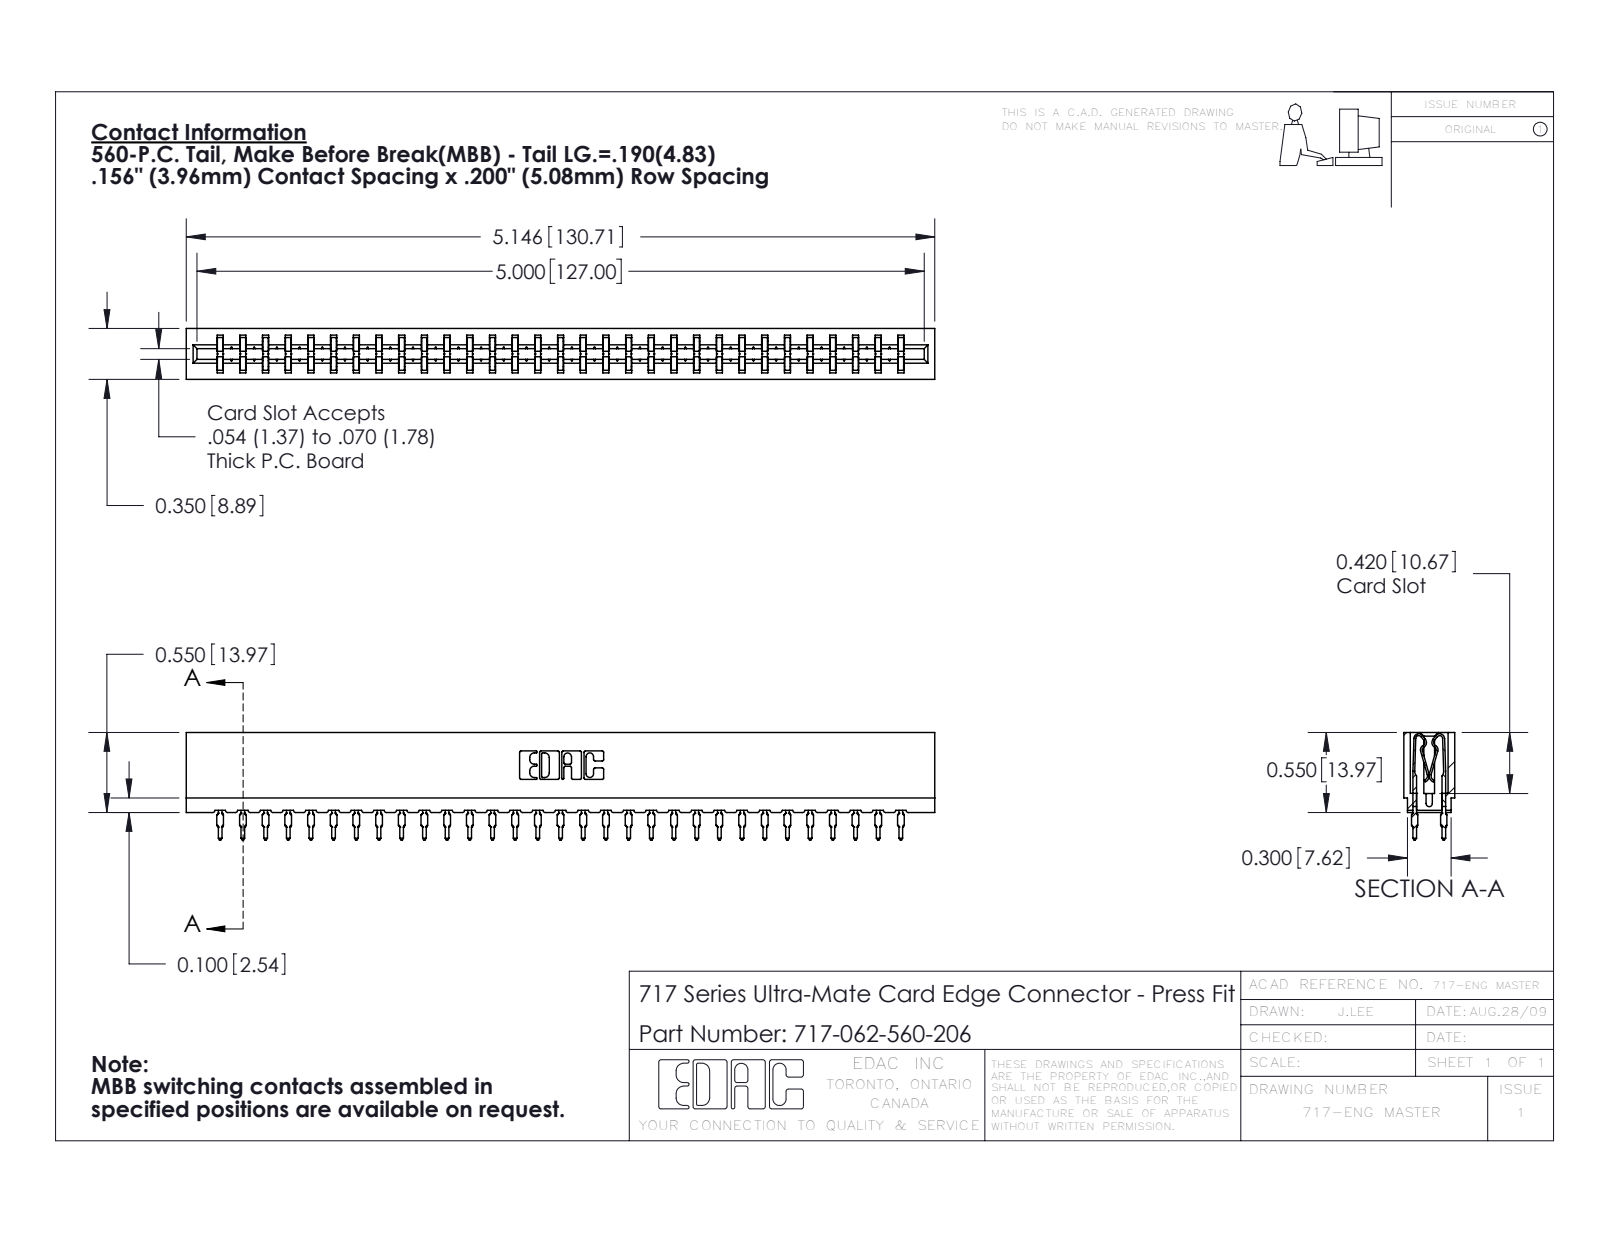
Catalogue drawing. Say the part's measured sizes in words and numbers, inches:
The part is named "717-062-560-206; 745-292-001_560; 717 Part_Insulator Option - 06". Its 3-D file was written by "SolidWorks 2016 (CONFIG_CONTROL_DESIGN)". It is 63 solids with 6232 faces: 3247 planar, 1373 cylindrical and 1612 other. Overall it measures 5.146 by 0.739 by 0.35 inches. Its volume is 0.708 cubic inches and its surface area 28.97 square inches. Partial cylindrical surfaces (rounded edges, fillets, slot ends): 124 of radius 0.021, 62 of radius 0.015, 22 of radius 0.01, 8 of radius 0.005, 8 of radius 0.011, 6 of radius 0.007, 6 of radius 0.031, 3 of radius 0.026. The main face-to-face distances are 0.212, 0.138, 0.35, 0.063, 0.287, 0.076, 0.149, 0.074, 0.045, 0.305.
